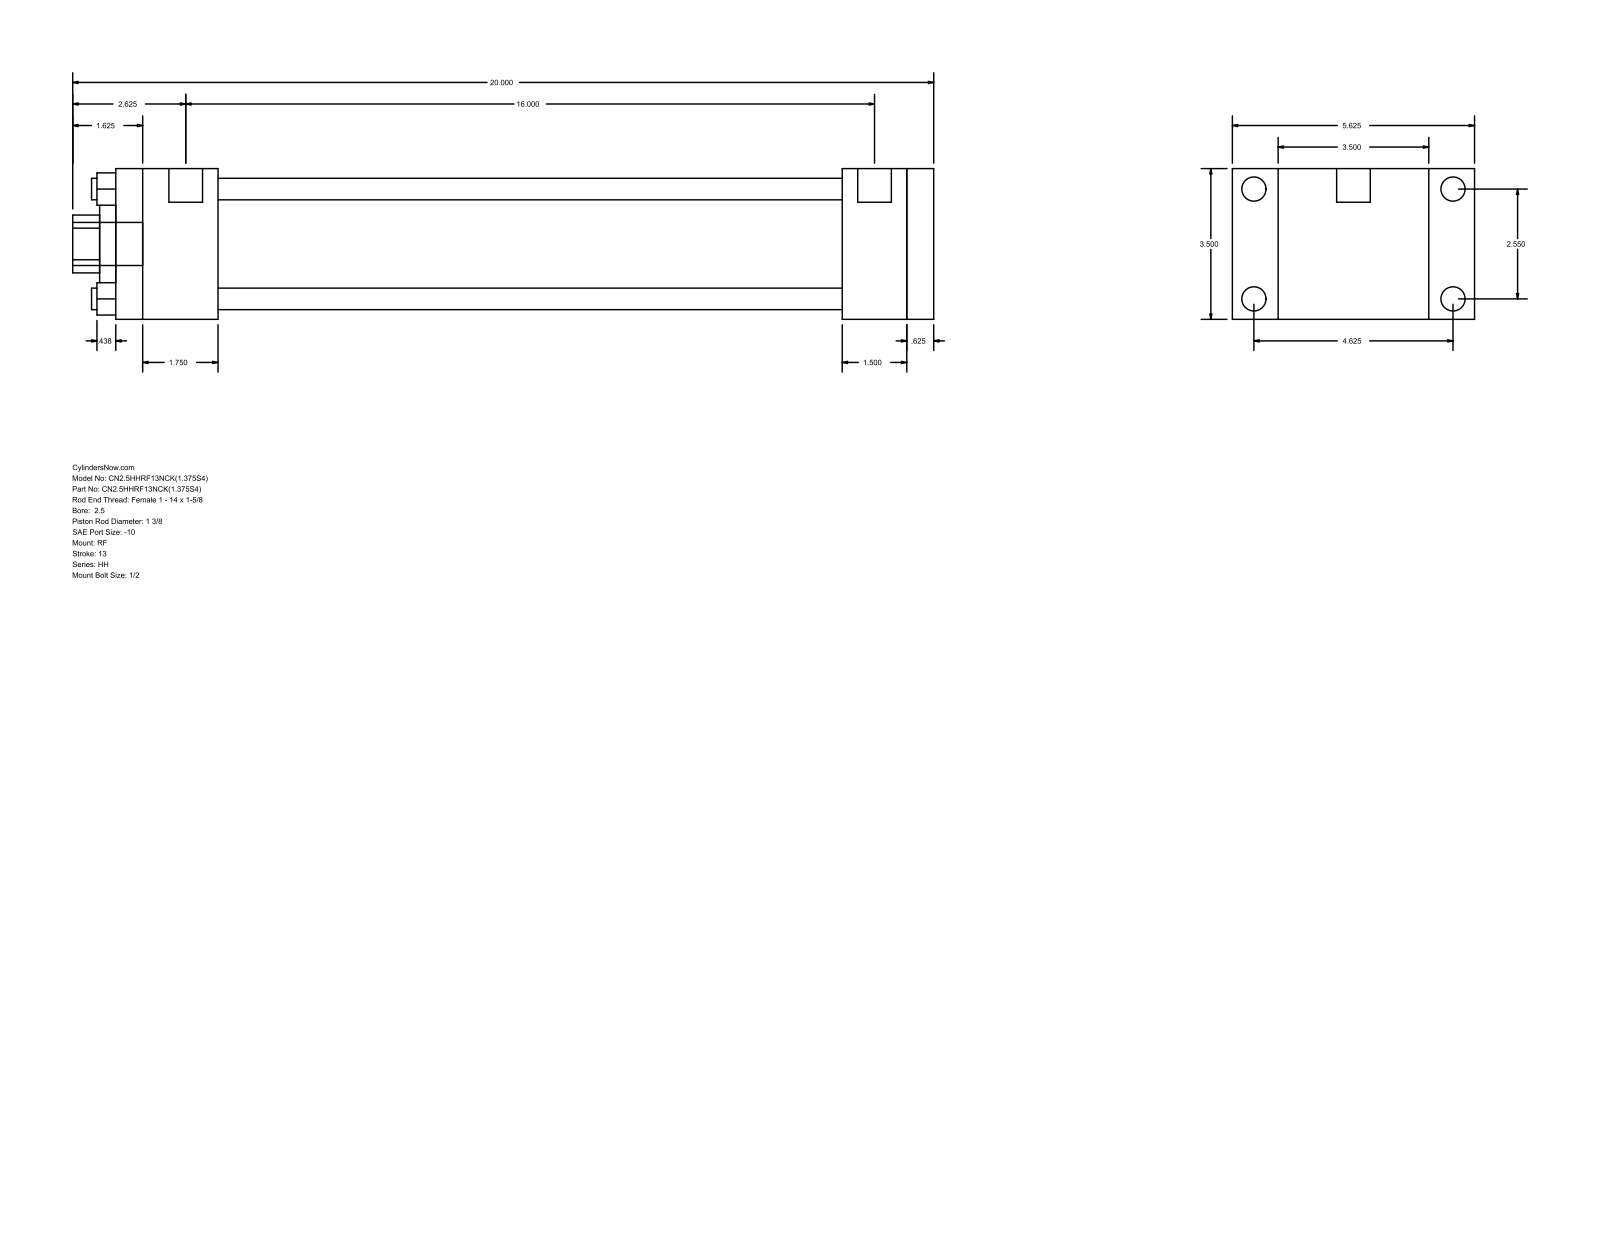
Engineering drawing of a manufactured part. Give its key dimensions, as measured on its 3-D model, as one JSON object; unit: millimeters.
{"part_name": "HH_RF__0250_1.375", "step_written_by": "GSSL Pune (CONFIG_CONTROL_DESIGN)", "units": "millimeters", "bodies": {"solids": 0, "faces": 92, "planar": 64, "cylindrical": 28, "other": 0}, "overall_size": [508, 142.88, 88.9], "round_holes": [[12.7, 4], [34.92, 1], [50.8, 1], [73.03, 1]], "round_bosses_or_shafts": [[14.3, 4], [5.56, 4], [19.84, 2], [25.4, 1]], "partial_cylinders_radius": [[17.06, 1]], "face_to_face_distances": [88.9, 482.6, 15.88, 466.72, 60.32, 406.4, 422.28, 428.62, 368.3, 38.1], "hole_center_spacings": [45.79, 64.76, 91.58]}
